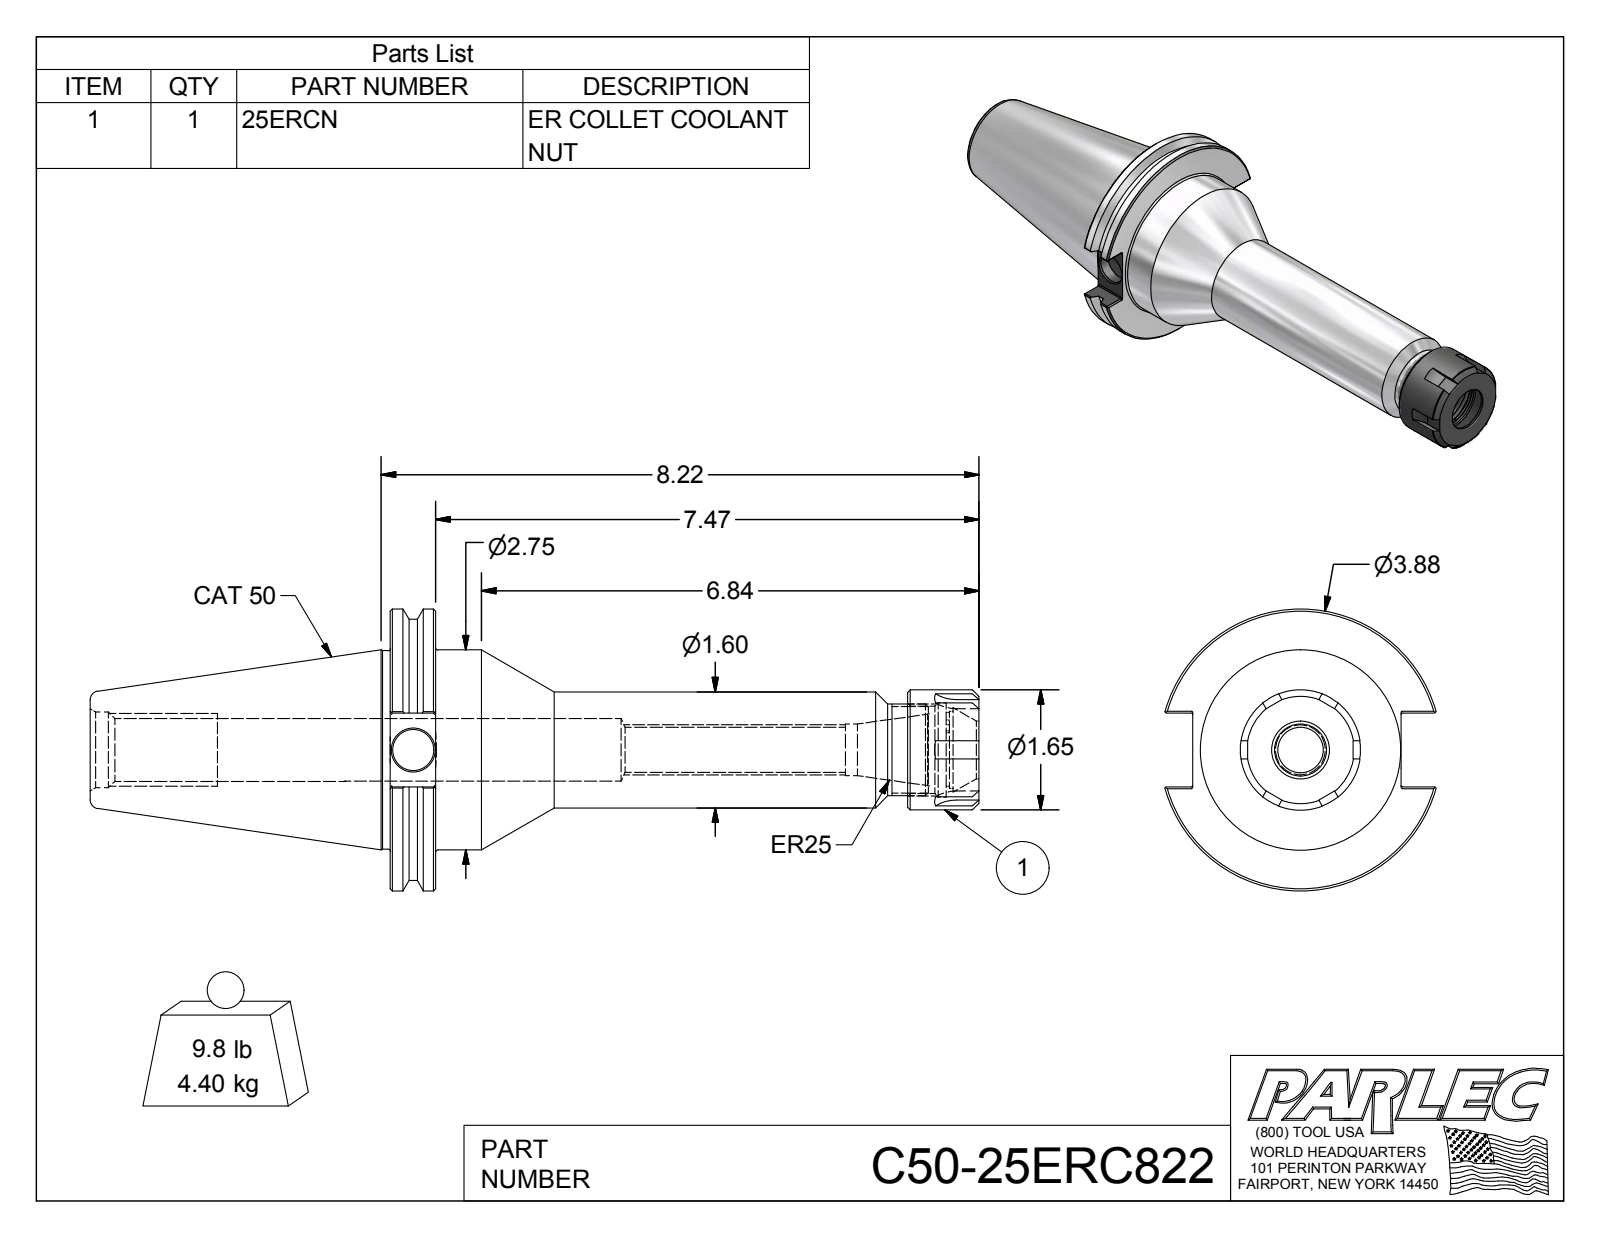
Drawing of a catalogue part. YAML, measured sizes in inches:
part_name: "C50-25ERC822; C50-25ER8-1; 25ERCN"
step_written_by: "Autodesk Inventor 2012 (AUTOMOTIVE_DESIGN)"
units: inches
bodies: {solids: 2, faces: 137, planar: 56, cylindrical: 41, other: 40}
overall_size: [12.22, 3.875, 3.729]
volume: 34.7
surface_area: 130.1
round_holes:
  - {diameter: 0.315, count: 1}
  - {diameter: 0.399, count: 1}
  - {diameter: 0.62, count: 1}
  - {diameter: 0.71, count: 1}
  - {diameter: 0.794, count: 1}
  - {diameter: 0.864, count: 1}
  - {diameter: 0.865, count: 1}
  - {diameter: 1.038, count: 1}
  - {diameter: 1.057, count: 1}
  - {diameter: 1.201, count: 1}
  - {diameter: 1.294, count: 1}
round_bosses_or_shafts:
  - {diameter: 3.875, count: 1}
  - {diameter: 3.594, count: 1}
  - {diameter: 2.75, count: 1}
  - {diameter: 2.73, count: 1}
  - {diameter: 1.654, count: 1}
  - {diameter: 1.595, count: 1}
  - {diameter: 1.26, count: 1}
partial_cylinders:
  - {radius: 0.02, count: 8}
  - {radius: 0.5, count: 6}
  - {radius: 0.472, count: 1}
  - {radius: 0.515, count: 1}
face_to_face_distances: [0.625, 8.095, 7.47, 7.111, 6.486, 0.984, 7.642, 7.017, 0.531, 0.453]
